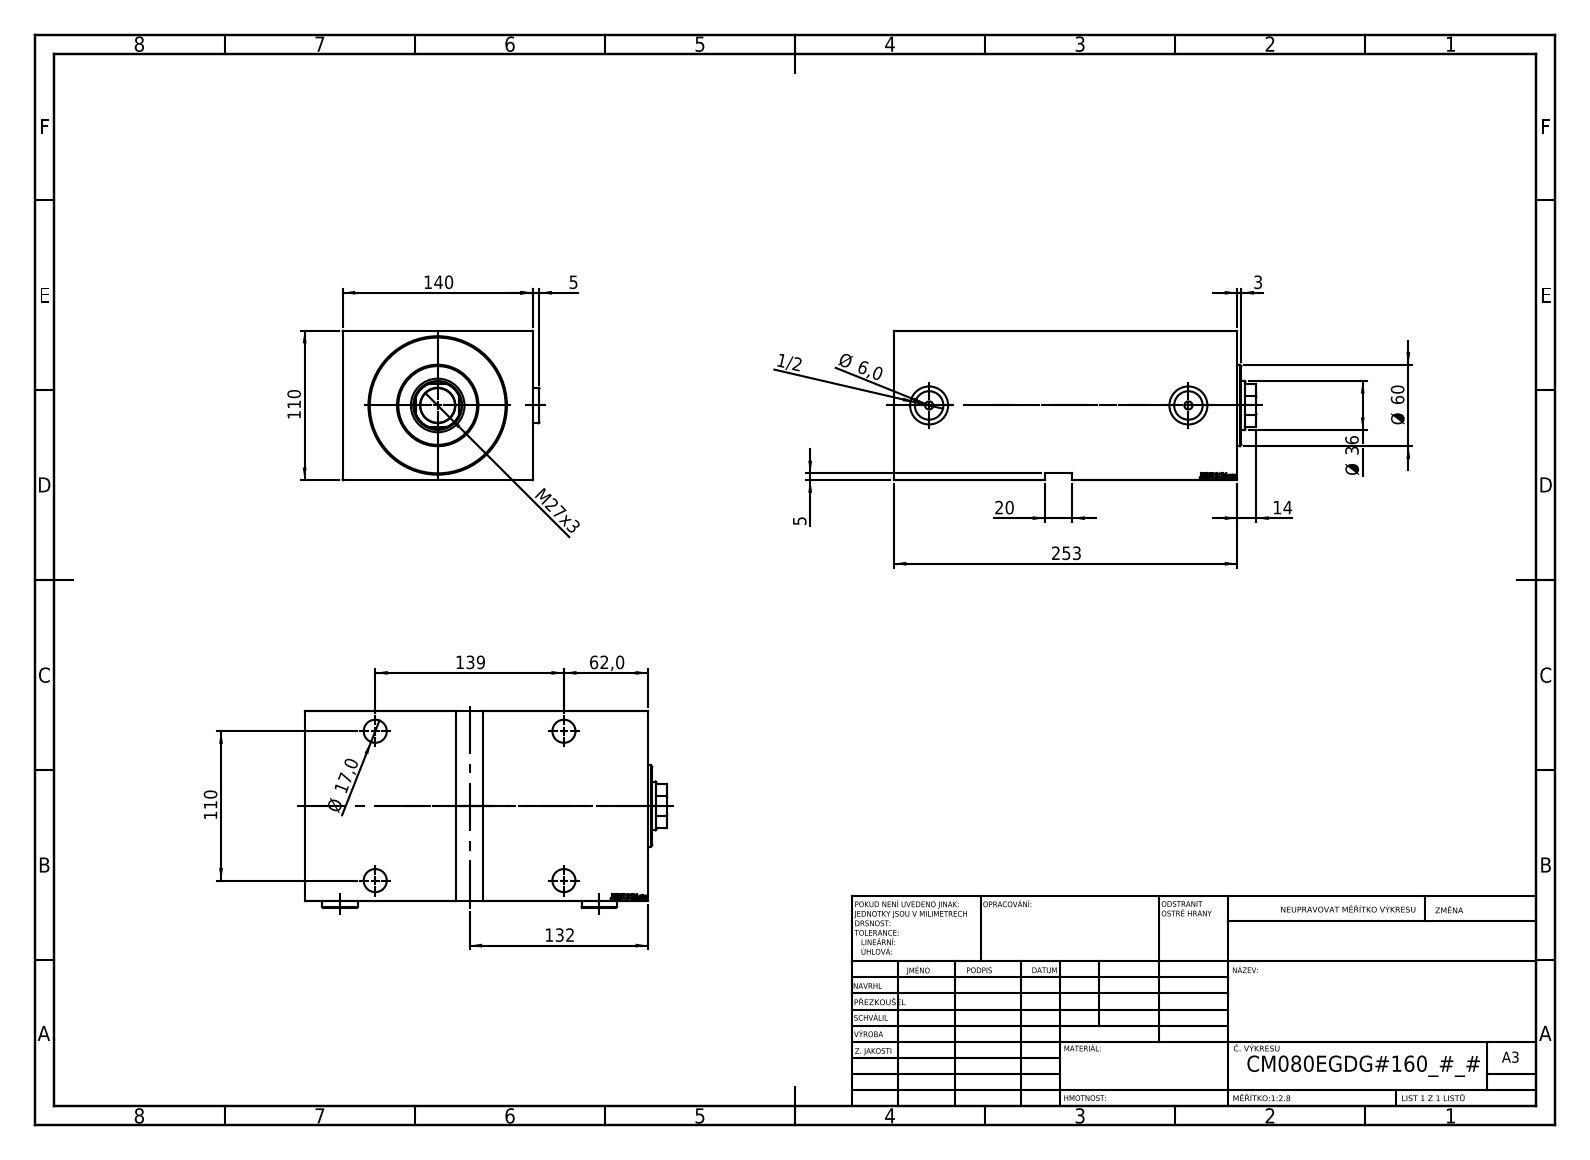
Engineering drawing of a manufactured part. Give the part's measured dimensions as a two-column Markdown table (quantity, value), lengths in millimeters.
| quantity | value |
| --- | --- |
| part name | Zatka_OIL_PORT; V450CM_VC_B; V450CM_E_Body; V450CM_E_VCP |
| STEP written by | SolidWorks 2019 (CONFIG_CONTROL_DESIGN) |
| units | millimeters |
| bodies | 5 solids, 912 faces (446 planar, 68 cylindrical, 398 other) |
| overall size | 267 × 144.9 × 110 |
| volume | 3 113 000 mm³ |
| surface area | 317 913 mm² |
| round holes (diameter × count) | 17 × 4, 25 × 4, 6 × 2, 20.96 × 2, 28 × 2, 25.5 × 1, 36 × 1, 39.5 × 1, 80 × 1, 100 × 1 |
| round bosses / shafts (diameter × count) | 26 × 2, 82 × 1, 60 × 1 |
| partial cylindrical surfaces (radius × count) | 17.5 × 1 |
| main face-to-face distances | 110, 140, 253, 21, 232, 5, 248, 227, 79, 236.4 |
| hole center spacings | 110, 139, 177.26, 191 |
